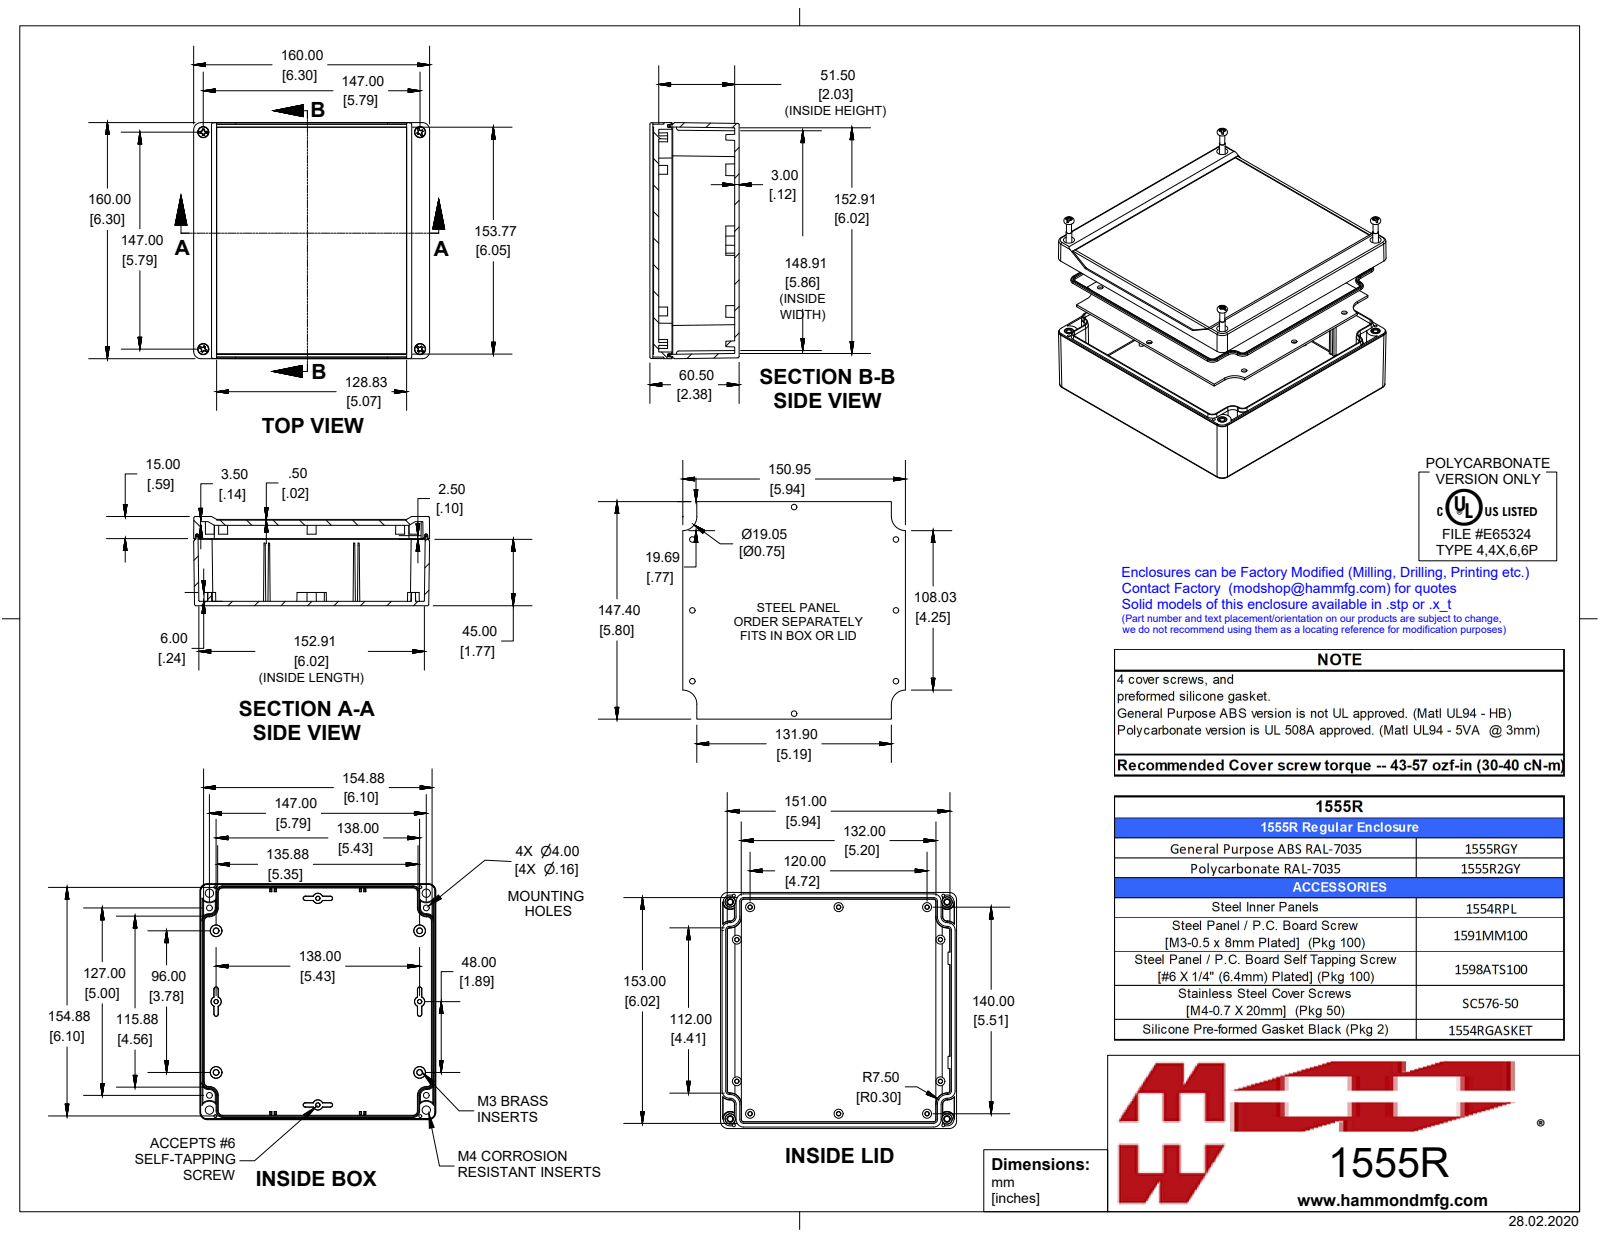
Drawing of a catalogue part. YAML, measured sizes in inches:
part_name: "1555R2GY"
step_written_by: "SolidWorks 2019 (AUTOMOTIVE_DESIGN)"
units: inches
bodies: {solids: 16, faces: 1418, planar: 434, cylindrical: 340, other: 644}
overall_size: [6.299, 6.299, 2.382]
volume: 19.86
surface_area: 380.7
round_holes:
  - {diameter: 0.079, count: 8}
  - {diameter: 0.097, count: 4}
  - {diameter: 0.11, count: 4}
  - {diameter: 0.128, count: 4}
  - {diameter: 0.138, count: 4}
  - {diameter: 0.147, count: 4}
  - {diameter: 0.276, count: 4}
round_bosses_or_shafts:
  - {diameter: 0.25, count: 4}
  - {diameter: 0.236, count: 4}
  - {diameter: 0.218, count: 4}
  - {diameter: 0.21, count: 4}
  - {diameter: 0.19, count: 4}
  - {diameter: 0.154, count: 4}
  - {diameter: 0.153, count: 4}
  - {diameter: 0.15, count: 4}
partial_cylinders:
  - {radius: 0.02, count: 32}
  - {radius: 0.039, count: 8}
  - {radius: 0.197, count: 8}
  - {radius: 0.187, count: 4}
  - {radius: 0.375, count: 4}
  - {radius: 0.059, count: 2}
face_to_face_distances: [0.118, 0.236, 0.138, 0.354, 2.028, 1.791, 0.419, 0.3, 0.064, 2.283]
hole_center_spacings: [5.433, 2.851, 5.635, 5.699, 0.197, 1.019, 1.019, 1.176]
